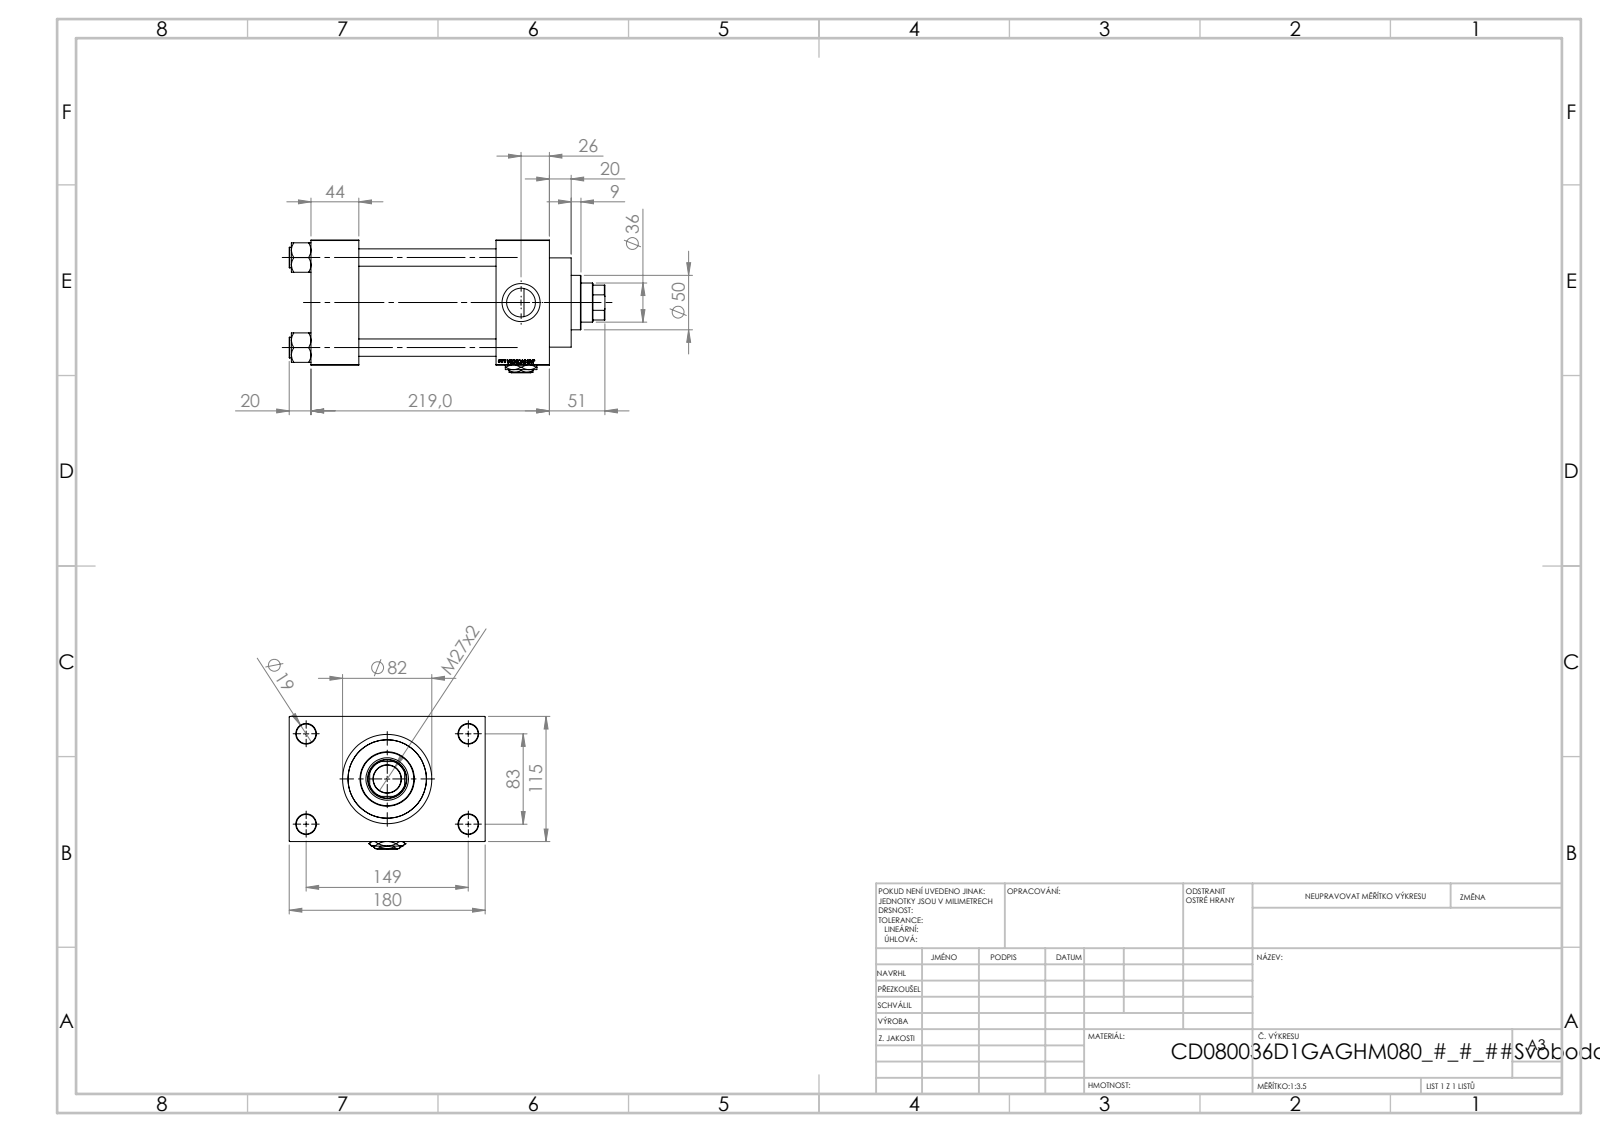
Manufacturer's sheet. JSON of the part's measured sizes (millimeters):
{"part_name": "V215CD_VC_A; V215CD_D_Body; V215CD_NUT_M5_D; V215CD_VCP_D (+2 more)", "step_written_by": "SolidWorks 2019 (CONFIG_CONTROL_DESIGN)", "units": "millimeters", "bodies": {"solids": 12, "faces": 1200, "planar": 569, "cylindrical": 93, "other": 538}, "overall_size": [290, 180, 122], "volume_mm3": 2125000, "surface_area_mm2": 349667, "round_holes": [[16, 4], [18, 4], [26.44, 3], [35, 3], [7, 2], [25.5, 1], [36, 1], [39, 1], [61, 1], [72, 1], [80, 1]], "round_bosses_or_shafts": [[19, 4], [86, 1], [82, 1], [50, 1]], "partial_cylinders_radius": [[17.5, 1]], "face_to_face_distances": [115, 126, 175, 49, 44, 170, 219, 32.5, 147.5, 180], "hole_center_spacings": [33.15, 58.48, 82.7, 85.28, 89.24, 115.85, 142.43, 83]}
